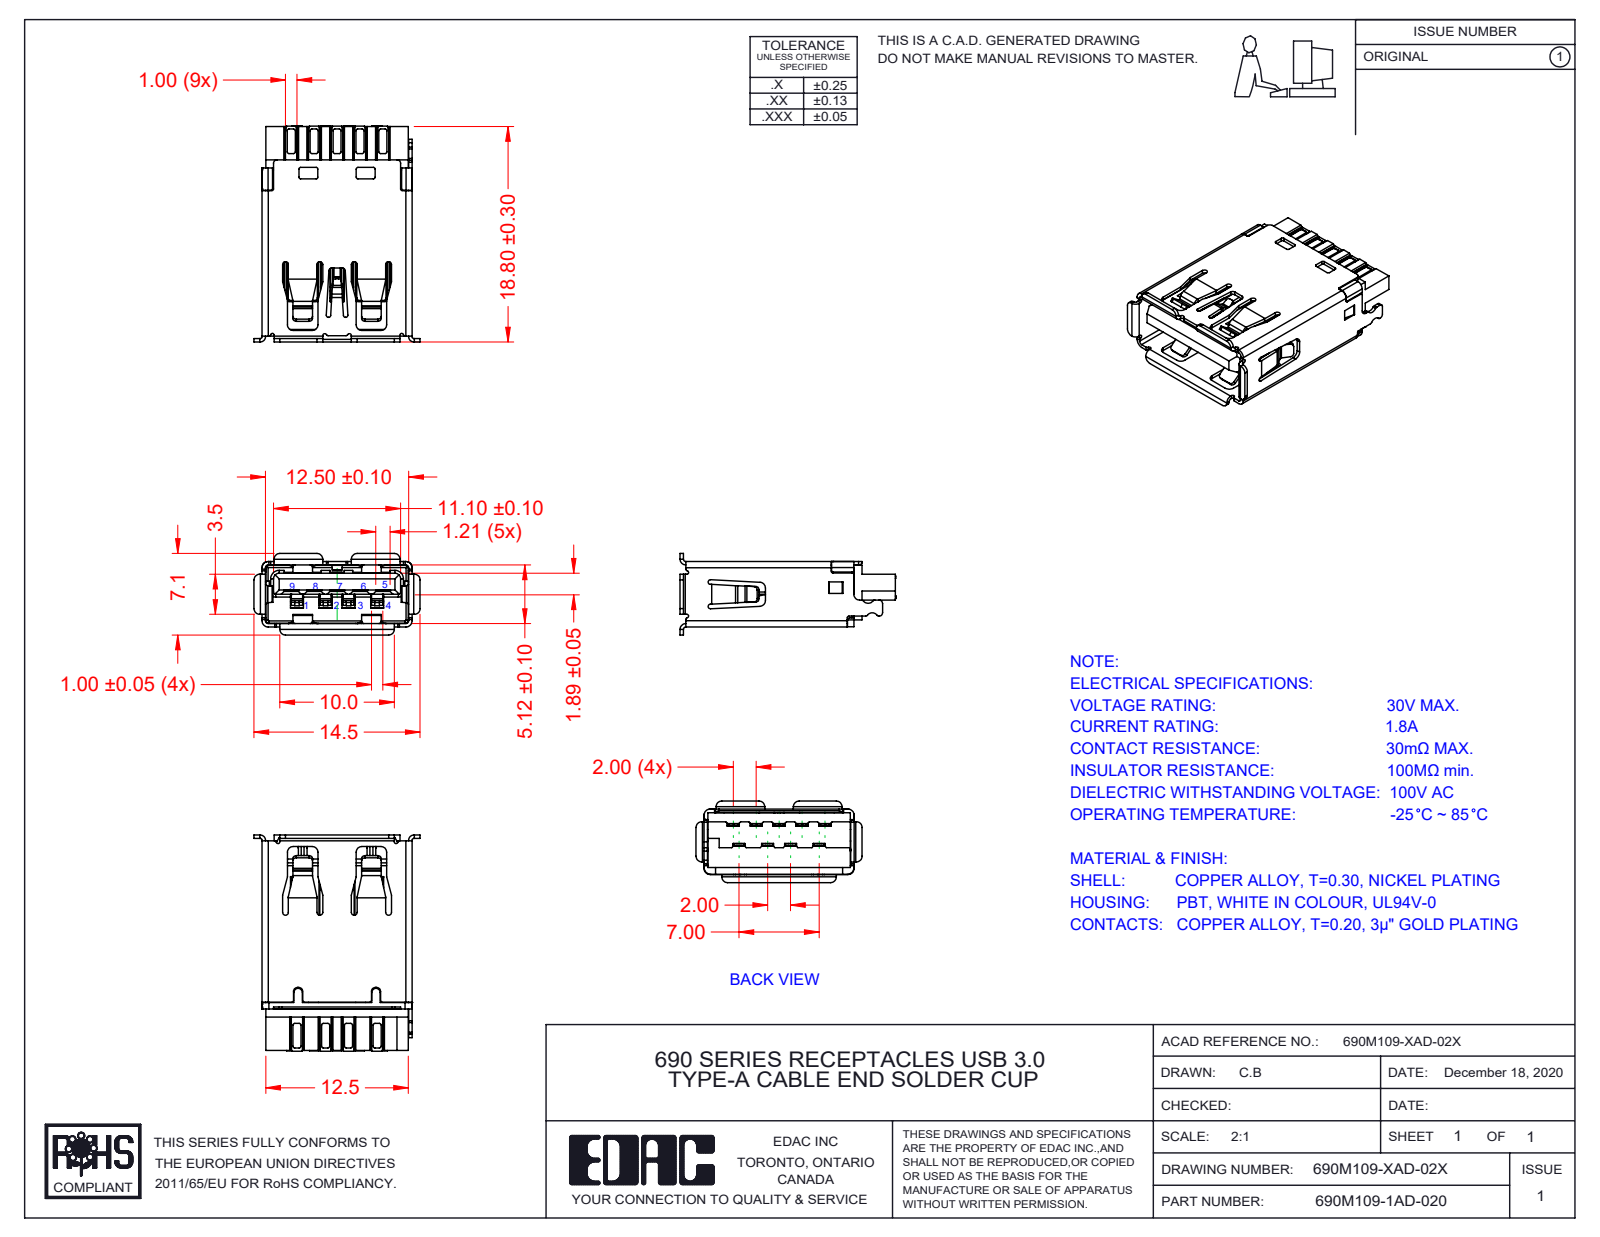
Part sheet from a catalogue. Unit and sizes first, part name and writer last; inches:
Units: inches
Overall size (bounding box): 0.743 × 0.571 × 0.28
Partial cylindrical surfaces — rounded edges, fillets, slot ends (radius × count): R0.006 ×128, R0.004 ×46, R0.008 ×36, R0.012 ×32, R0.005 ×30, R0.02 ×26, R0.01 ×20, R0.039 ×13
Main face-to-face distances: 0.213, 0.225, 0.202, 0.013, 0.101, 0.113, 0.046, 0.504, 0.079, 0.014
Volume: 0.039 in³ · Surface area: 4.289 in²
Bodies: 12 solids, 2114 faces (1344 planar, 654 cylindrical, 116 other)
Part name (STEP PRODUCT): Insulator2 690M109-XAD-02X_White; Insulator1 690M109-XAD-02X_White; Contact4 690M109-XAD-02X; Contact5 3.0 690M109-XAD-02X (+5 more)
STEP written by: SolidWorks 2020 (AUTOMOTIVE_DESIGN)
